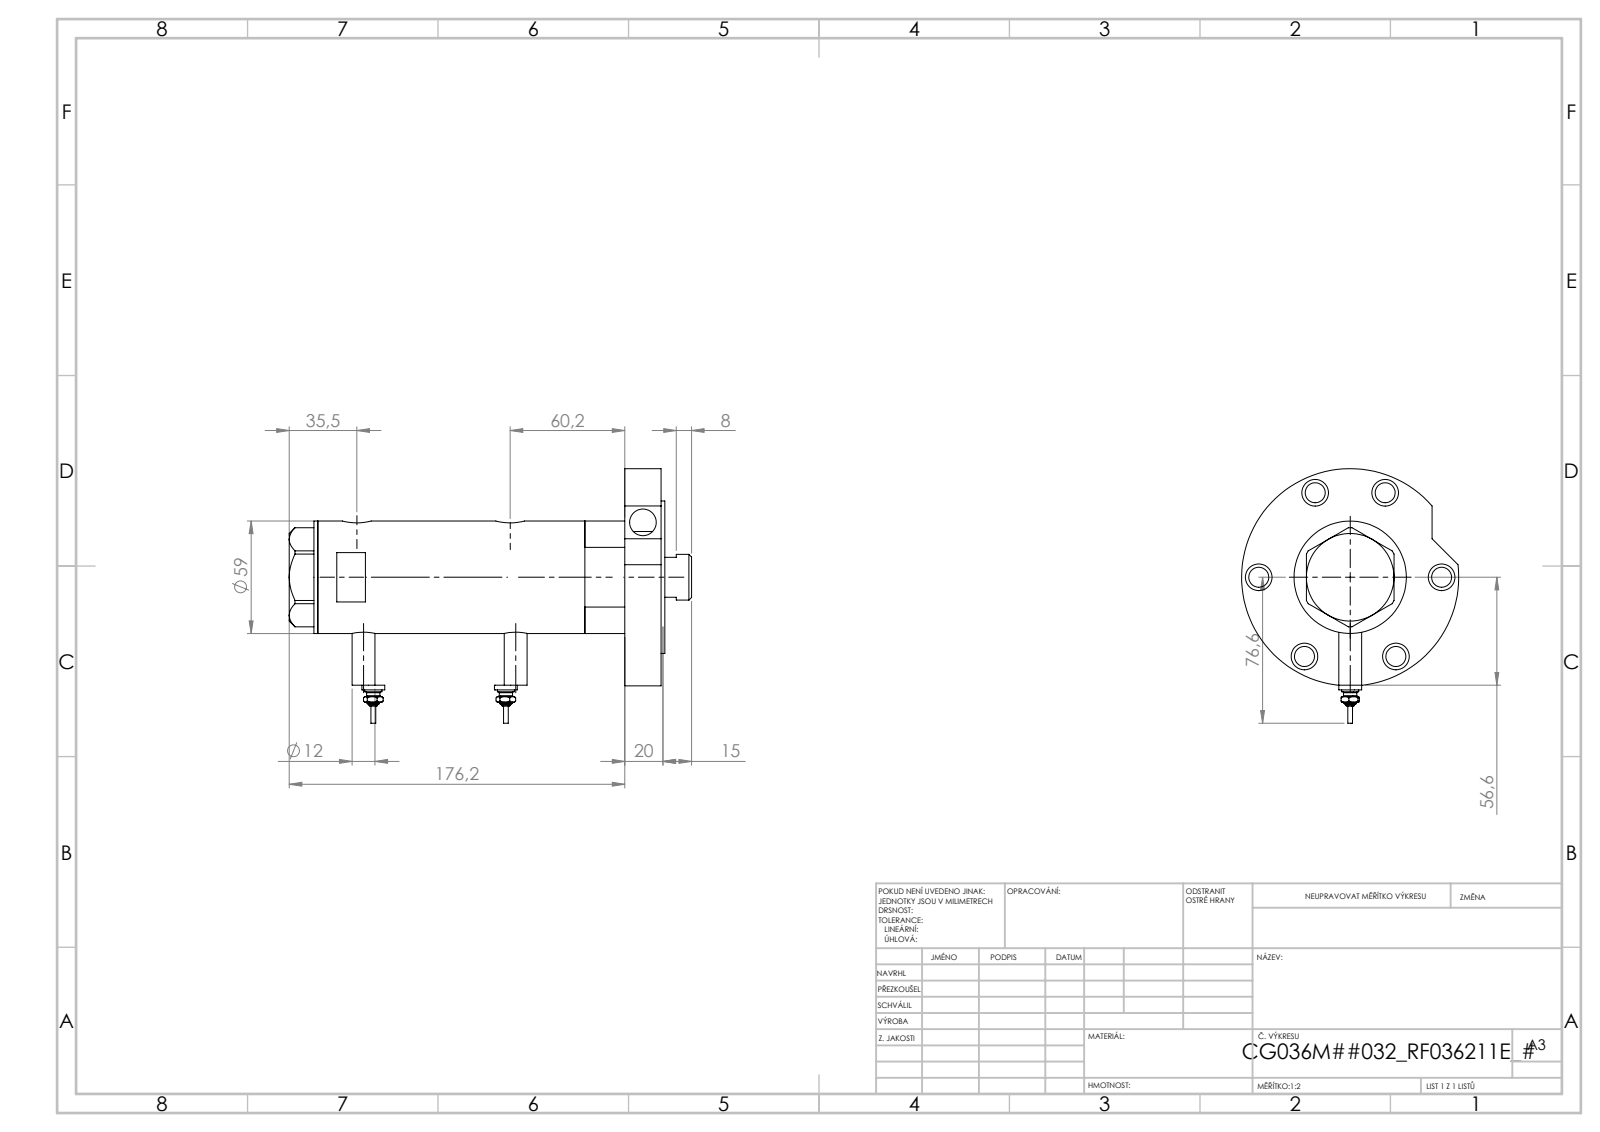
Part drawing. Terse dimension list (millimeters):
name: V270CG_MIDDLE; V270CG_VC; V270CG_RF211E; V270CG_BACK (+2 more)
written by: SolidWorks 2019 (CONFIG_CONTROL_DESIGN)
unit: mm
bodies: 7 solids, 256 faces (90 planar, 102 cylindrical, 64 other)
size: 211.2 × 133.6 × 114
volume: 630 126 mm³; area: 136 847 mm²
holes: 7× ⌀14, 6× ⌀10.5, 2× ⌀9.73, 2× ⌀12.5, 2× ⌀15, 1× ⌀8.5, 1× ⌀25, 1× ⌀26.5, 1× ⌀36, 1× ⌀40, 1× ⌀48, 1× ⌀52
bosses: 4× ⌀12, 2× ⌀9, 2× ⌀7, 2× ⌀4.5, 2× ⌀2.5, 1× ⌀114, 1× ⌀80, 1× ⌀59
face distances: 2, 19, 21, 182.2, 161.2, 180.2, 102.2, 59, 78, 80
hole spacings: 48, 53.34, 79.82, 83.14, 86.1, 95.8, 2.9, 3.5
